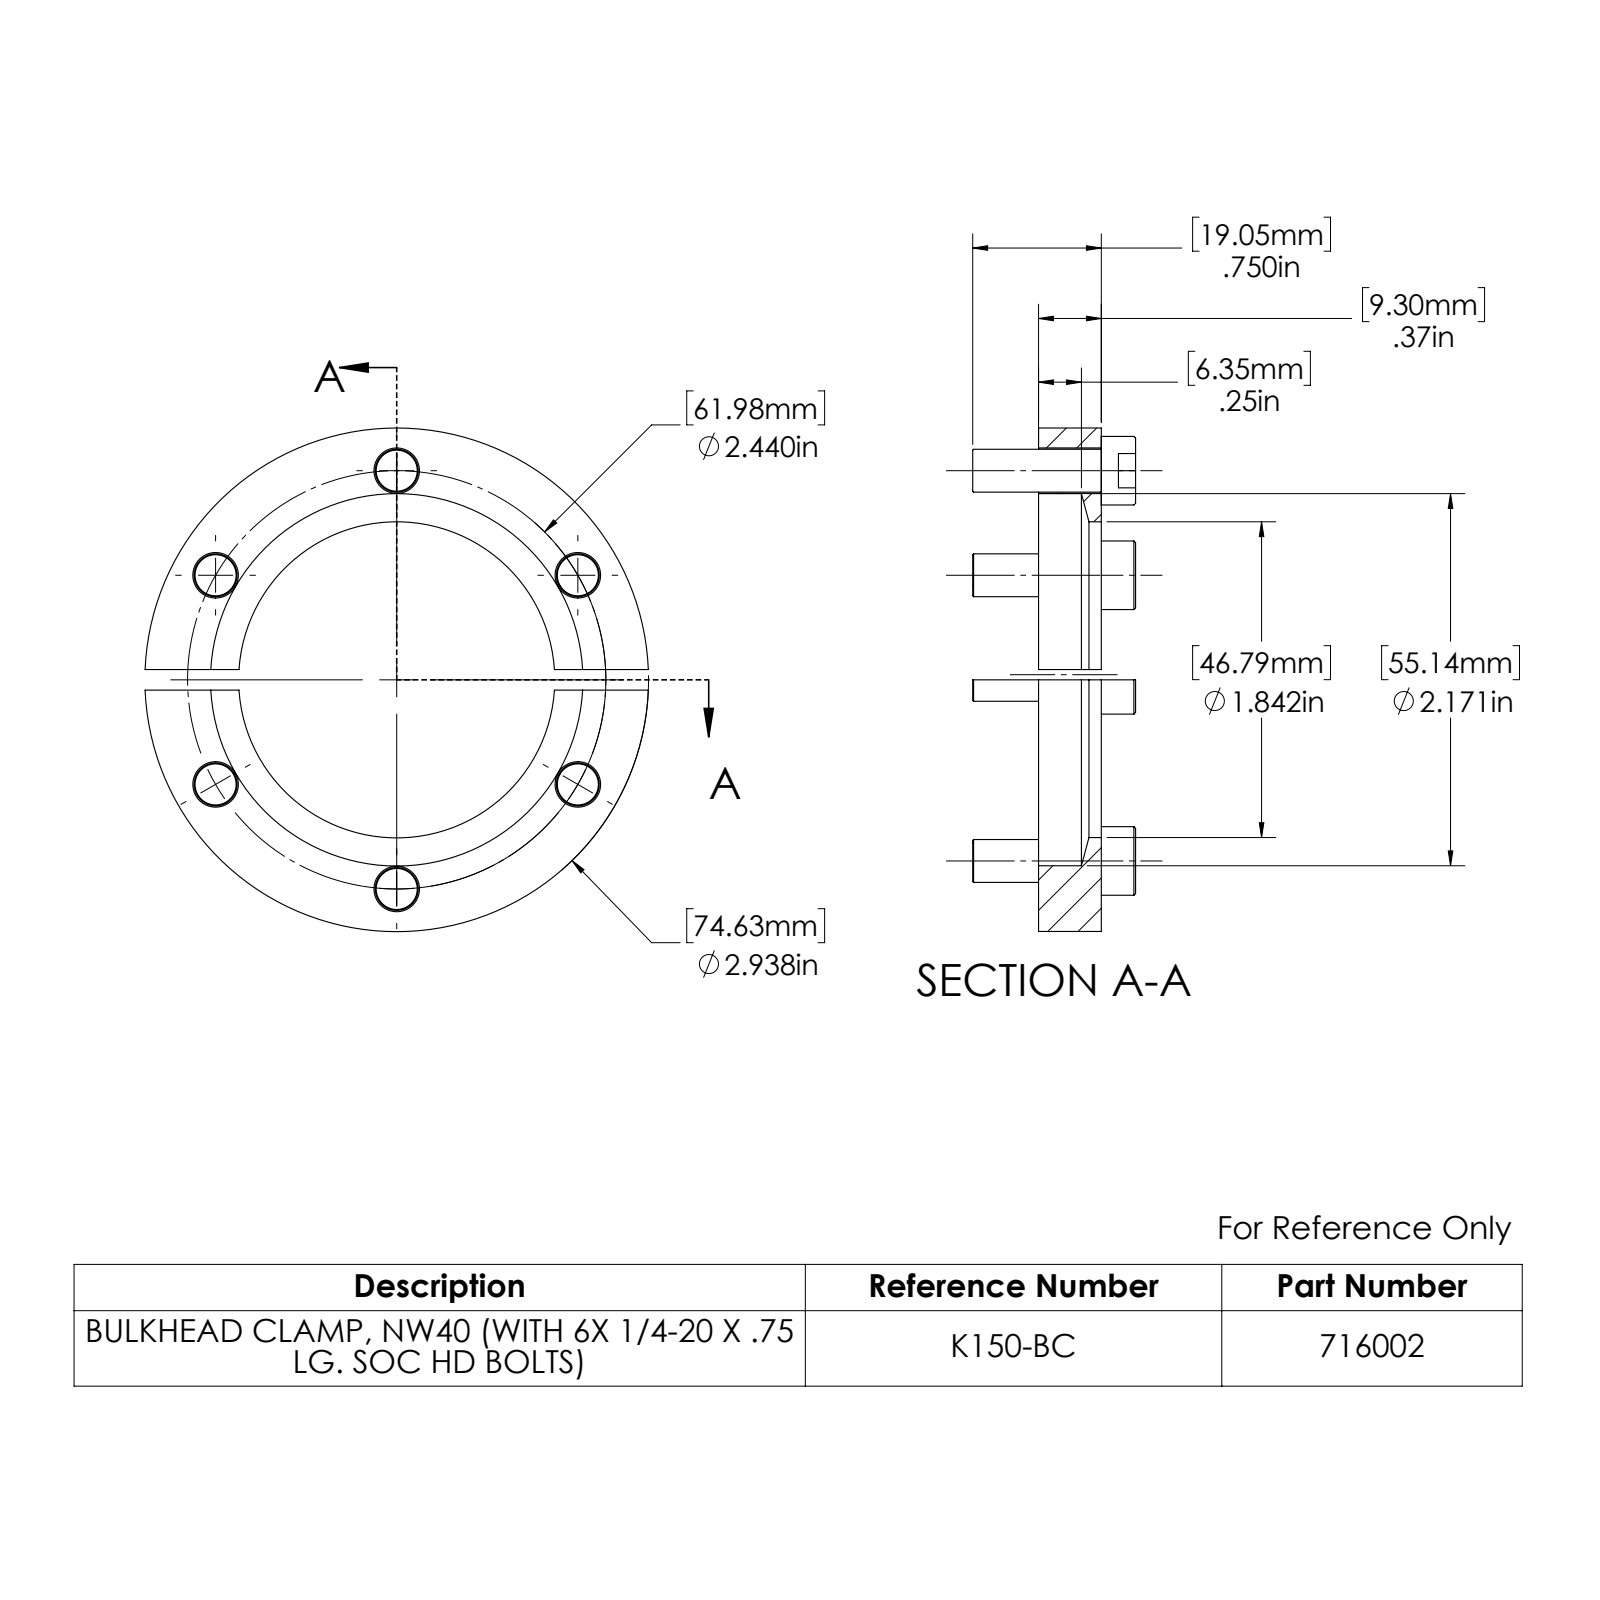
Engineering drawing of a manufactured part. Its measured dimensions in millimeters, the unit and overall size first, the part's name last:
Units: millimetres
Overall size (bounding box): 74.6 × 74.6 × 23.3
Round holes (diameter × count): ⌀6.8 ×6, ⌀46.8 ×1, ⌀55.2 ×1
Round bosses / shafts (diameter × count): ⌀10.2 ×6, ⌀6.4 ×6, ⌀74.6 ×1
Main face-to-face distances: 9.3, 5.1, 14.4, 2.5, 3, 8.9, 18.2, 23.3, 20.7, 11.8
Hole centre spacings: 31, 53.7, 62, 31, 53.7
Volume: 23 010 mm³ · Surface area: 14 100 mm²
Bodies: 8 solids, 140 faces (68 planar, 45 cylindrical, 27 other)
Part name (STEP PRODUCT): 716002
STEP written by: SolidWorks 2022 (AUTOMOTIVE_DESIGN)
